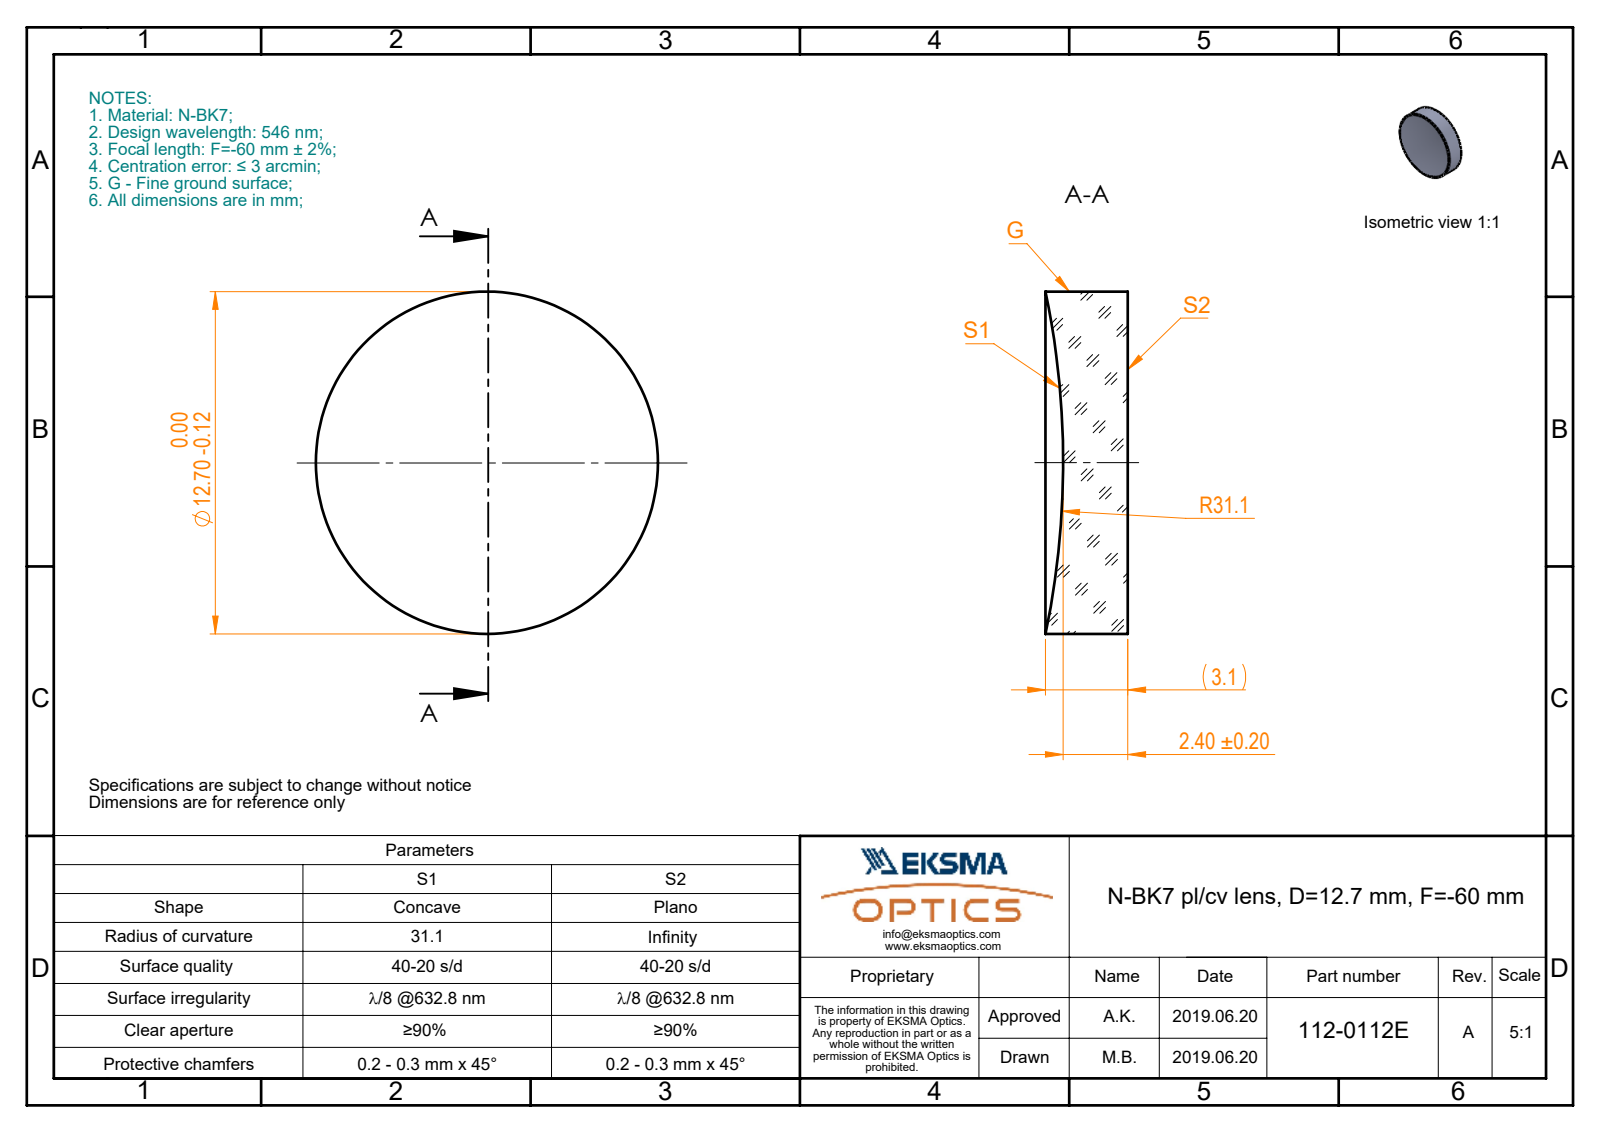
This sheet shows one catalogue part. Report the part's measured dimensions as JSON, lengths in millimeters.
{"part_name": "112-0112E BK7 pl-cv 12.7 F-60", "step_written_by": "SolidWorks 2017 (CONFIG_CONTROL_DESIGN)", "units": "millimeters", "bodies": {"solids": 1, "faces": 5, "planar": 1, "cylindrical": 2, "other": 2}, "overall_size": [12.7, 12.7, 3.06], "volume_mm3": 345, "surface_area_mm2": 377, "round_bosses_or_shafts": [[12.7, 1]]}
